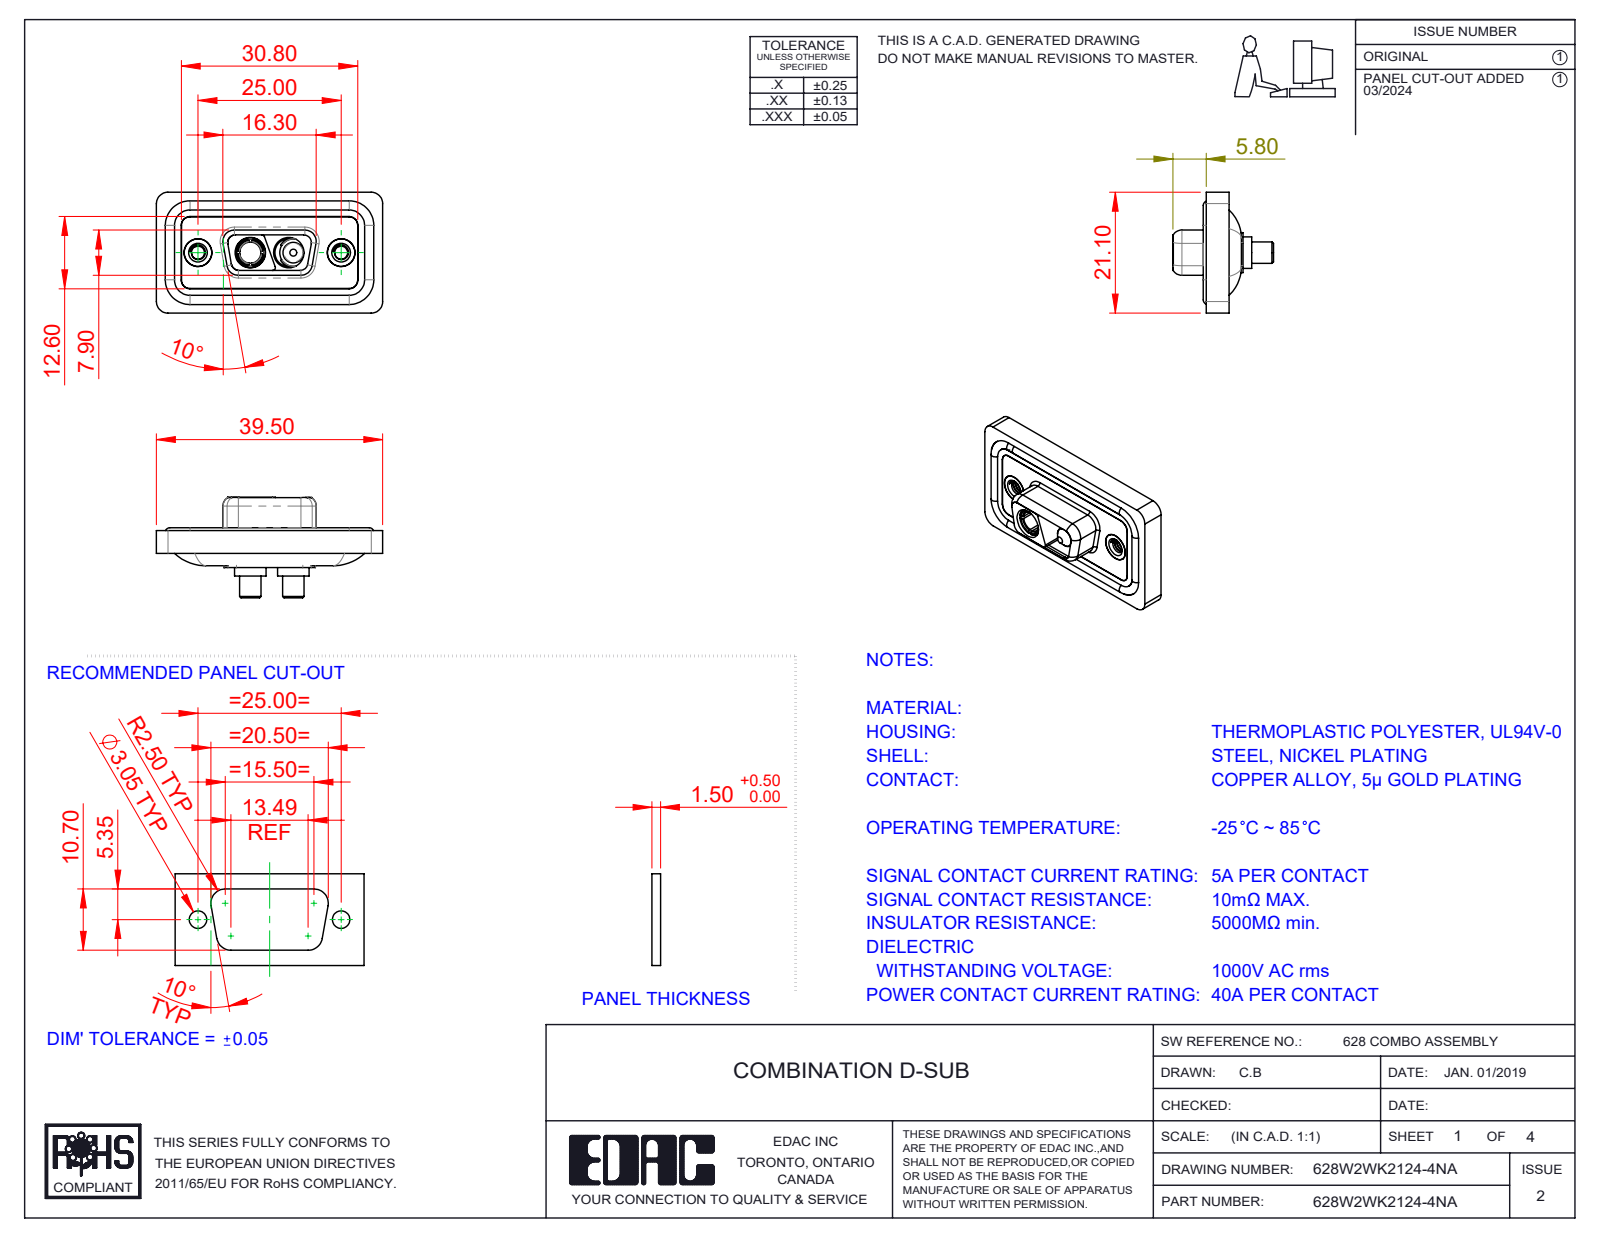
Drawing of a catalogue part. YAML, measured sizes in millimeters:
part_name: "628Combo Housing_2WK2; Power Socket_40A S; 628Combo Waterproof Housing_09 Contacts; 628Combo Shell Front_09 Contacts (+4 more)"
step_written_by: "SolidWorks 2023 (CONFIG_CONTROL_DESIGN)"
units: millimeters
bodies: {solids: 11, faces: 498, planar: 144, cylindrical: 233, other: 121}
overall_size: [39.5, 21.1, 17.55]
volume: 4642
surface_area: 7363
round_holes:
  - {diameter: 4.85, count: 4}
  - {diameter: 2.26, count: 2}
  - {diameter: 4, count: 2}
  - {diameter: 4.05, count: 2}
  - {diameter: 5, count: 2}
  - {diameter: 5.3, count: 2}
  - {diameter: 3.7, count: 1}
round_bosses_or_shafts:
  - {diameter: 1.6, count: 4}
  - {diameter: 5.5, count: 2}
  - {diameter: 5.2, count: 2}
  - {diameter: 4.95, count: 2}
  - {diameter: 4.8, count: 2}
  - {diameter: 4.75, count: 2}
  - {diameter: 3.75, count: 2}
  - {diameter: 4.96, count: 1}
partial_cylinders:
  - {radius: 1.5, count: 22}
  - {radius: 2, count: 18}
  - {radius: 1.35, count: 8}
  - {radius: 1.6, count: 8}
  - {radius: 0.5, count: 6}
  - {radius: 0.25, count: 4}
  - {radius: 0.6, count: 4}
  - {radius: 0.65, count: 4}
face_to_face_distances: [0.4, 1.1, 2.9, 1.6, 0.5, 1.8, 5.65, 5.35, 3.1, 1.5]
hole_center_spacings: [9.14, 15.86, 6.72, 25]
